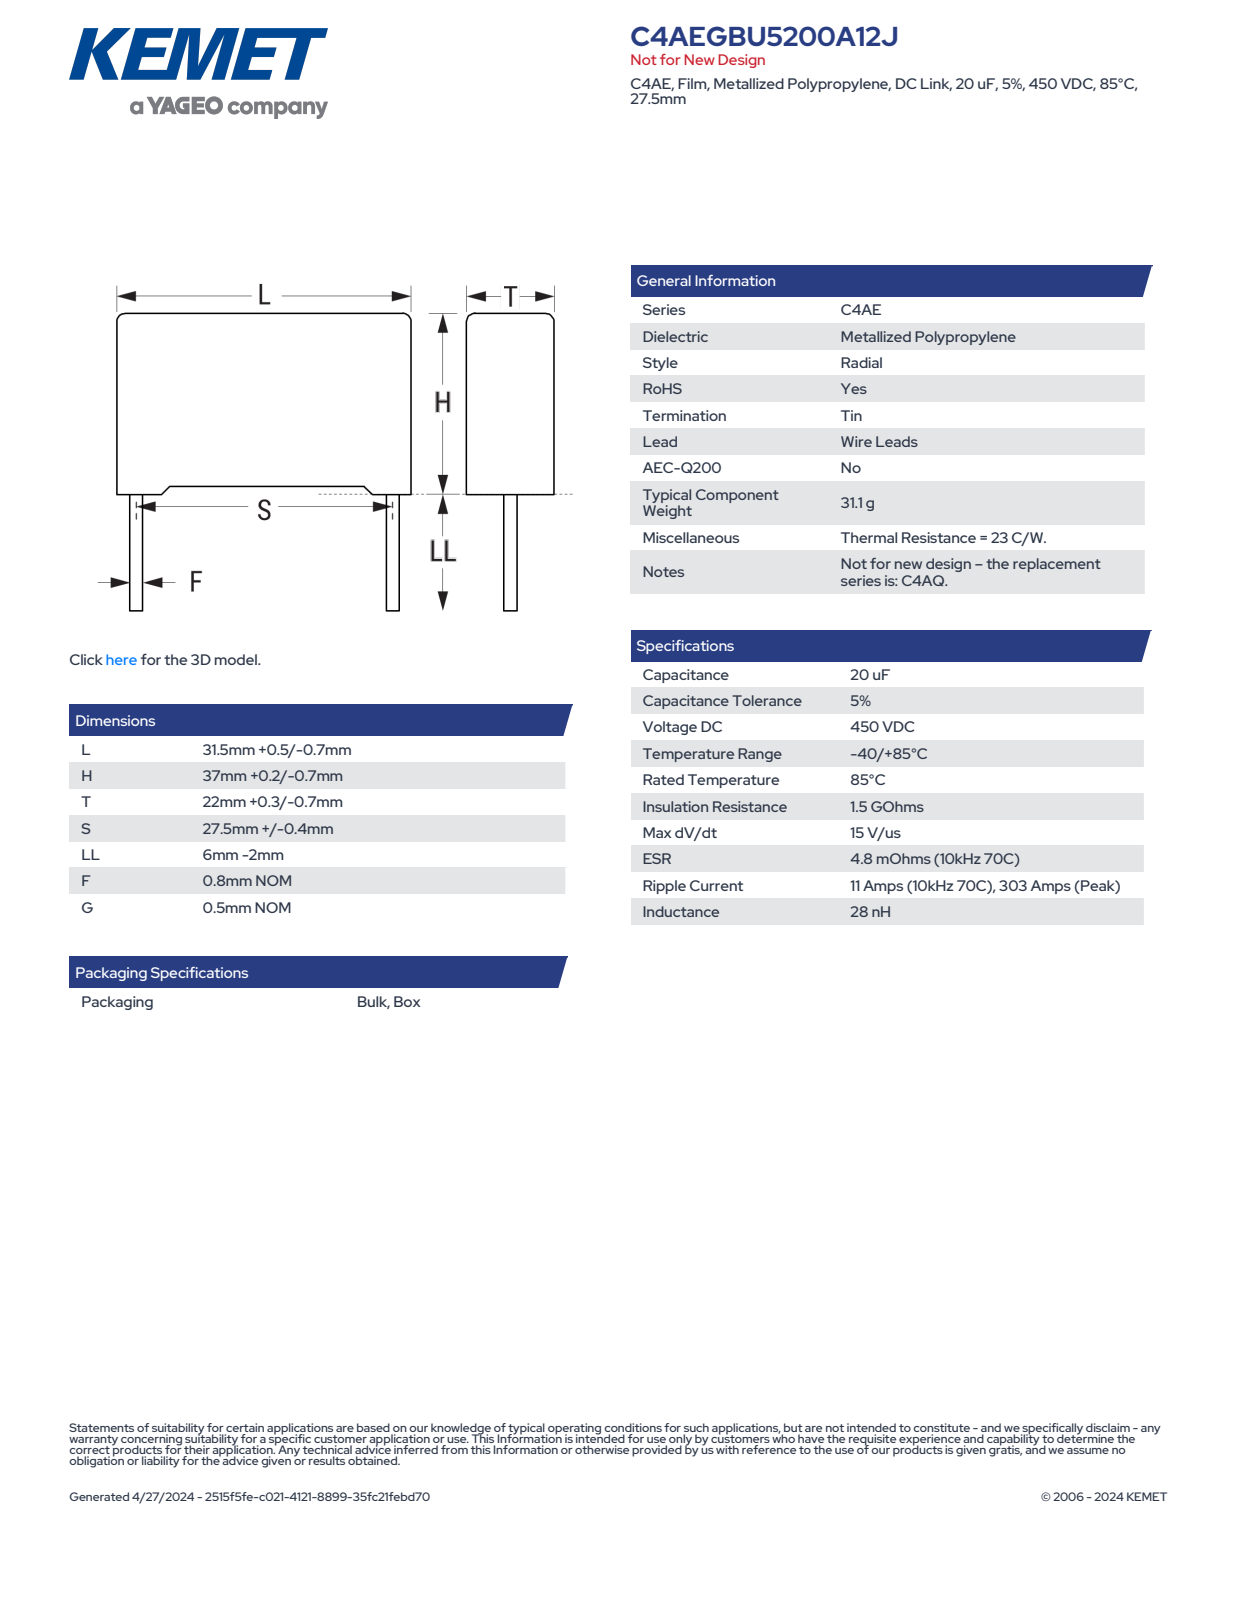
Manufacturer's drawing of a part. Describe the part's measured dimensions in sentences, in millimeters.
The part is named "CFR_RB2CFP_31.5X37X22_L32H37.2T22.3S27.5LL4F0.8". Its 3-D file was written by "SolidWorks 2014 (AUTOMOTIVE_DESIGN)". It is 4 solids with 85 faces: 77 planar, 8 cylindrical and 0 other. Overall it measures 41.2 by 32 by 22.3 millimeters. Its volume is 25 781 cubic millimeters and its surface area 5 537 square millimeters. Round bosses or shafts: 2 of diameter 0.8. Partial cylindrical surfaces (rounded edges, fillets, slot ends): 4 of radius 0.5. The main face-to-face distances are 22.3, 32, 35.92, 0.53, 36.45, 0.75, 1.28, 37.2, 1.07, 30.93.
